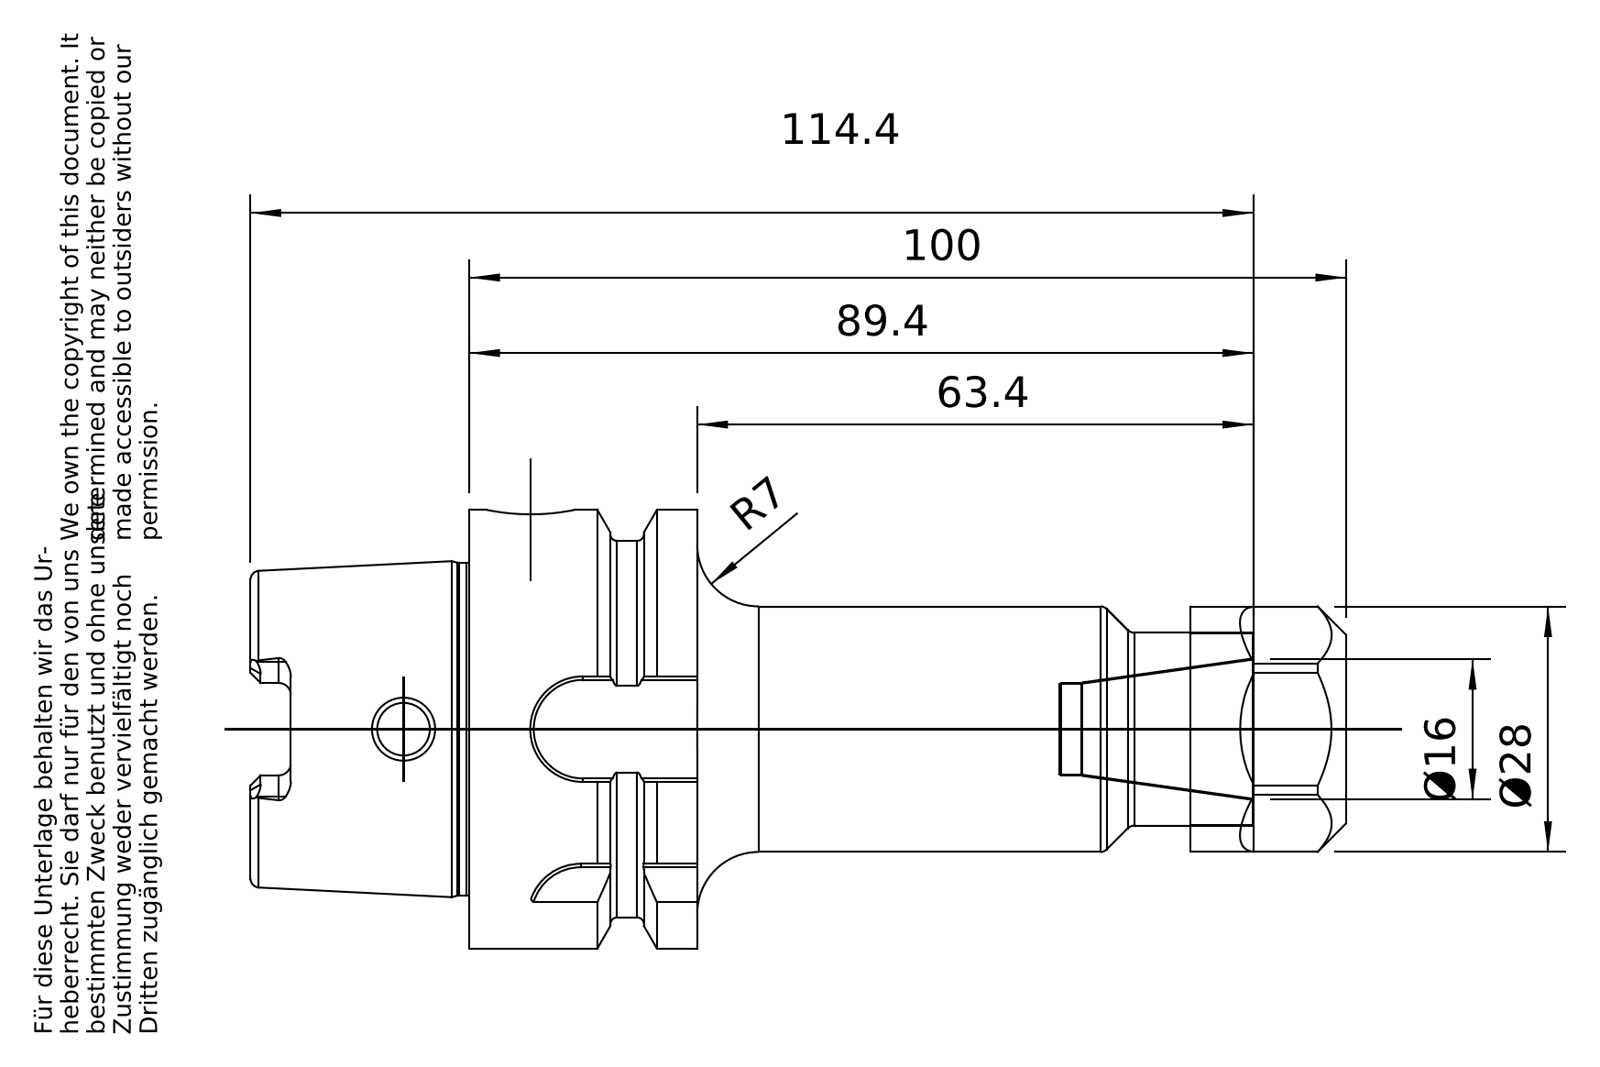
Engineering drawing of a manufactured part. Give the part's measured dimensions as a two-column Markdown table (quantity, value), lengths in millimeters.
| quantity | value |
| --- | --- |
| part name | A50-020-16; 83-912-16; A50-020-16_ASM |
| STEP written by | PRO/ENGINEER BY PARAMETRIC TECHNOLOGY CORPORATION, 2010430 (CONFIG_CONTROL_DESIGN) |
| units | millimeters |
| bodies | 2 solids, 217 faces (72 planar, 53 cylindrical, 92 other) |
| overall size | 124.9 × 50 × 50 |
| volume | 92 256 mm³ |
| surface area | 23 581 mm² |
| round holes (diameter × count) | 6 × 1, 10 × 1, 10.5 × 1, 14 × 1, 16 × 1, 16.32 × 1, 16.5 × 1, 26.04 × 1, 32.08 × 1 |
| round bosses / shafts (diameter × count) | 50 × 1, 42.95 × 1, 37.91 × 1, 28 × 1, 22 × 1 |
| partial cylindrical surfaces (radius × count) | 1.4 × 6, 2.38 × 4, 6 × 3, 6.02 × 1 |
| main face-to-face distances | 82.2, 25.95, 56.25, 25, 100, 74.05, 17.8, 8.4, 33.4, 24.9 |
